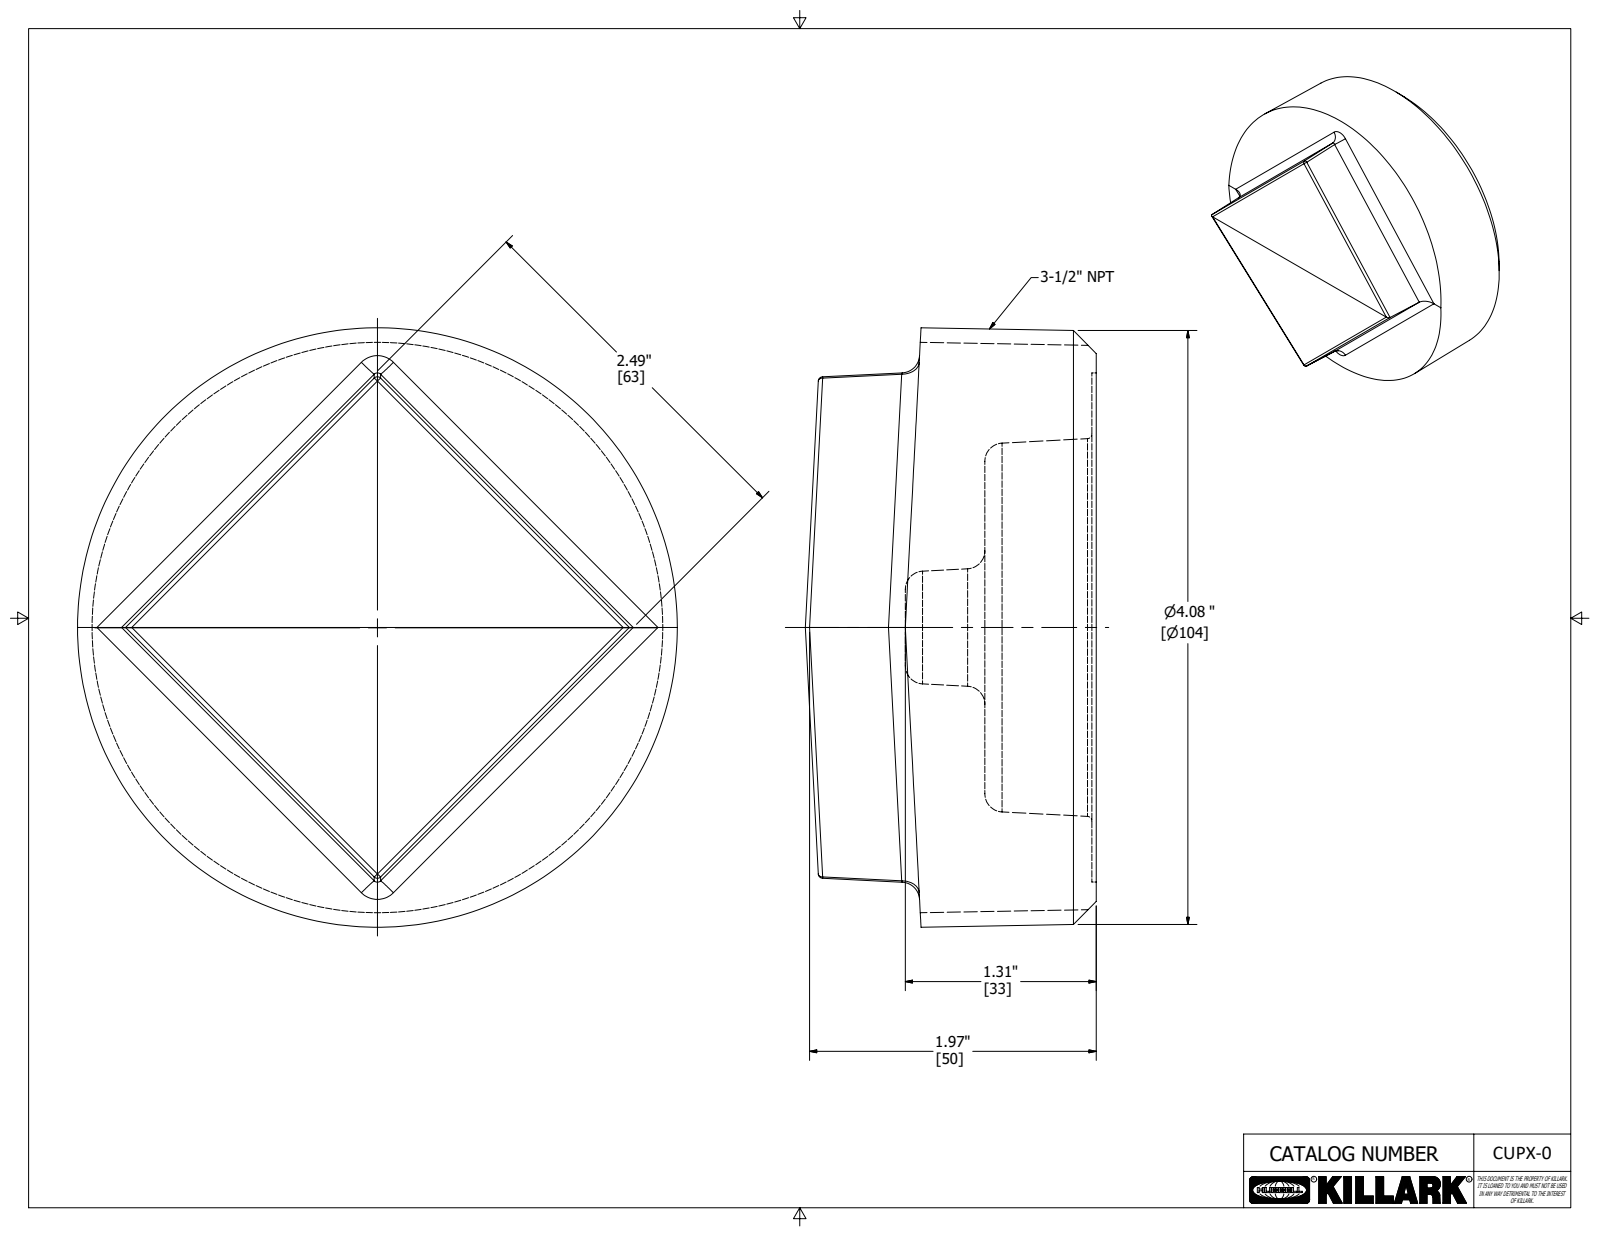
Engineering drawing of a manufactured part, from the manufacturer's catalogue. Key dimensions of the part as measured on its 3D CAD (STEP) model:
Part name (STEP PRODUCT): CUPX-0
STEP written by: Autodesk Inventor 2020 (AUTOMOTIVE_DESIGN)
Units: inches
Bodies: 1 solid, 35 faces (12 planar, 11 cylindrical, 12 other)
Overall size (bounding box): 4.125 × 4.121 × 2
Volume: 16.49 in³ · Surface area: 53.8 in²
Round holes (diameter × count): ⌀3.5 ×1
Partial cylindrical surfaces — rounded edges, fillets, slot ends (radius × count): R0.031 ×6, R0.125 ×4
Main face-to-face distances: 0.736, 0.687, 0.687, 0.766, 0.03, 0.547, 1.283, 1.313
